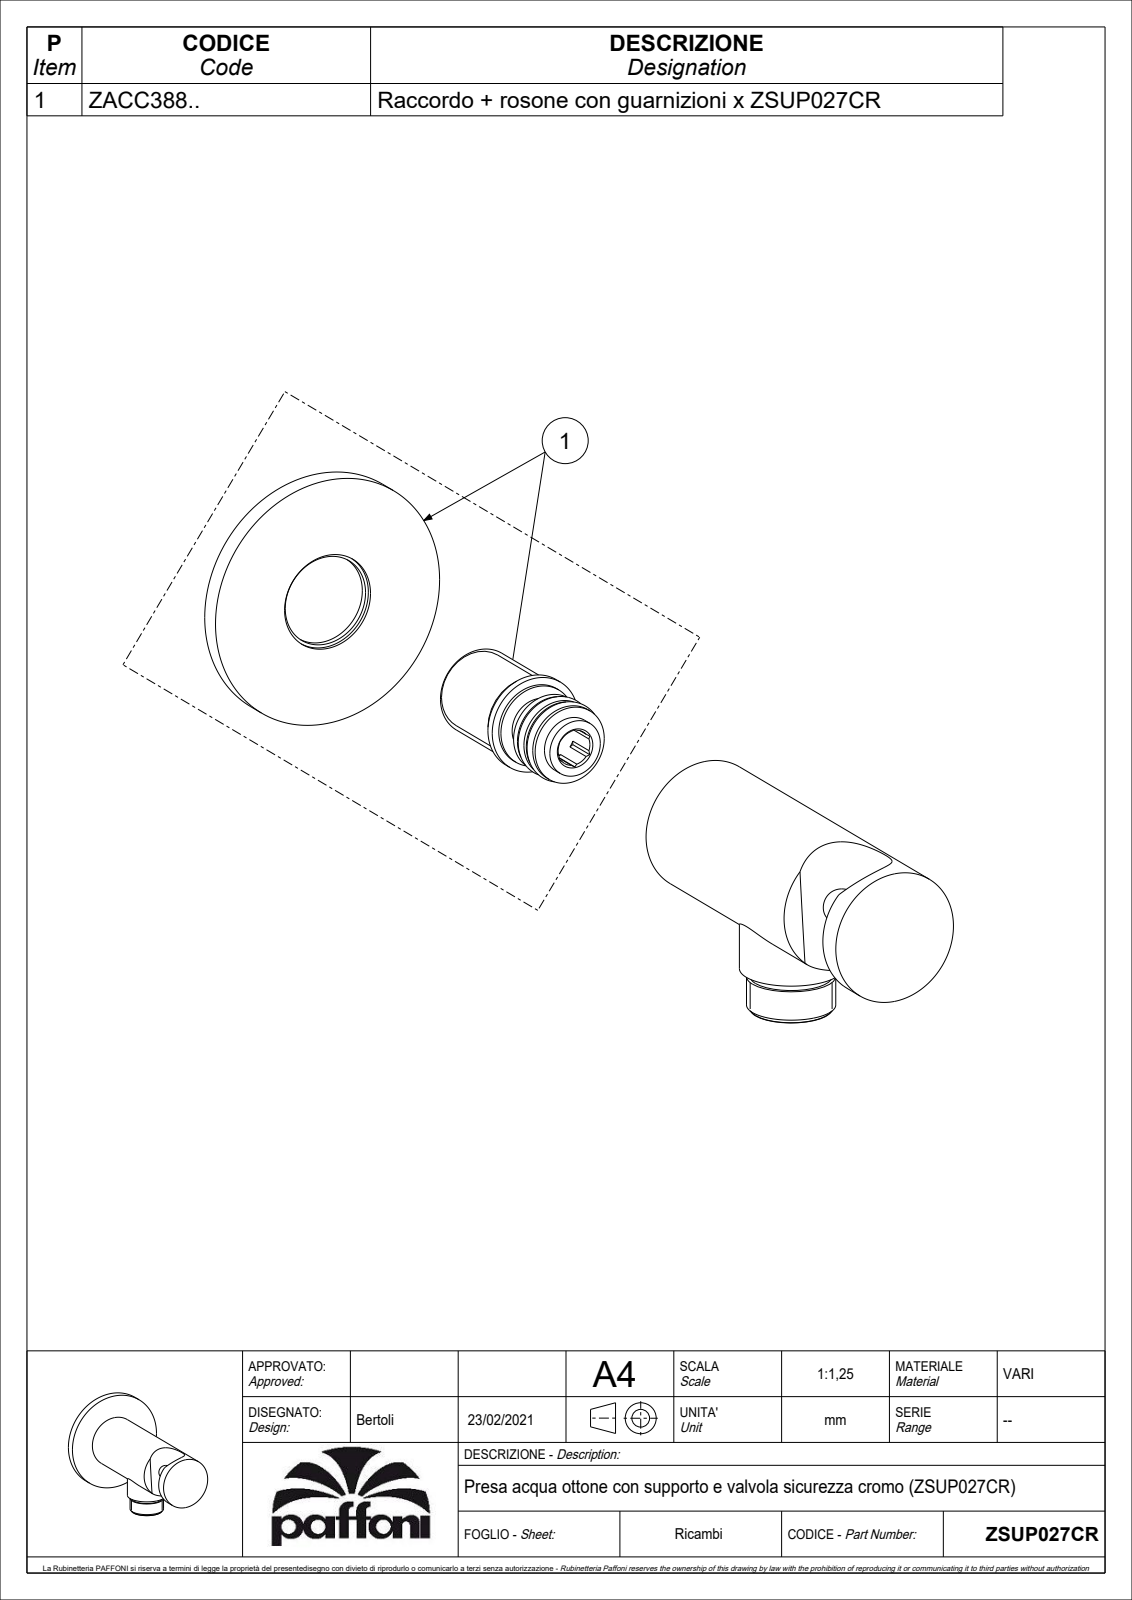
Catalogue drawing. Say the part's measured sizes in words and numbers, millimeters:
The part is named "ZSUP027CR". Its 3-D file was written by "CREO PARAMETRIC BY PTC INC, 2020044 (CONFIG_CONTROL_DESIGN)". It is 2 solids with 75 faces: 32 planar, 33 cylindrical and 10 other. Overall it measures 93 by 62.75 by 60 millimeters. Its volume is 62 227 cubic millimeters and its surface area 21 396 square millimeters. Round holes: 2 of diameter 15, 1 of diameter 3.3, 1 of diameter 5.5, 1 of diameter 6.5, 1 of diameter 8.5, 1 of diameter 18.5, 1 of diameter 19.5, 1 of diameter 21.5, 1 of diameter 23, 1 of diameter 34, 1 of diameter 54. Round bosses or shafts: 1 of diameter 60, 1 of diameter 31.5, 1 of diameter 24, 1 of diameter 20.7. The main face-to-face distances are 4.9, 2.5, 92.9, 88, 2.4, 90.5, 5, 93, 1.5, 52.
